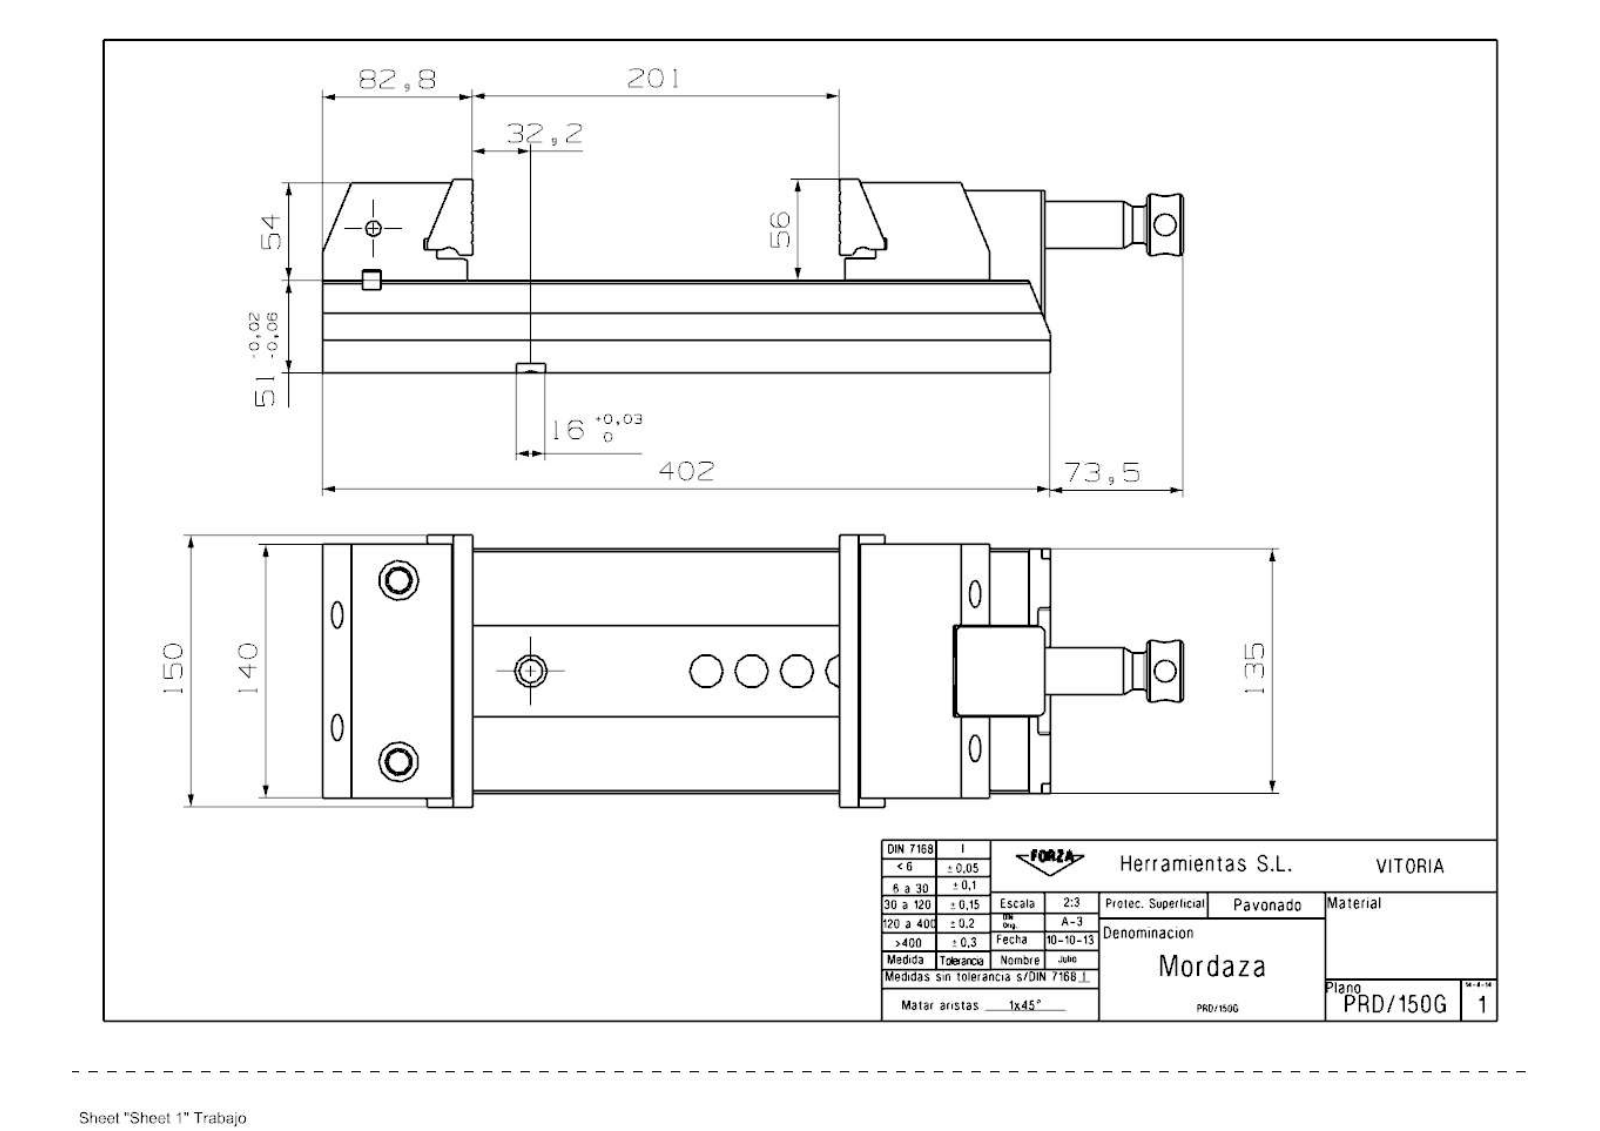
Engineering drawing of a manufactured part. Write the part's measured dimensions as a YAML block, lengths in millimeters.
part_name: "PRD_150G_Mordaza"
step_written_by: "SIEMENS PLM Software NX 9.0 (CONFIG_CONTROL_DESIGN)"
units: millimeters
bodies: {solids: 12, faces: 425, planar: 285, cylindrical: 92, other: 48}
overall_size: [475.5, 150, 107.1]
volume: 3171000
surface_area: 447778
round_holes:
  - {diameter: 13, count: 6}
  - {diameter: 15, count: 6}
  - {diameter: 5.19, count: 5}
  - {diameter: 6.99, count: 4}
  - {diameter: 8.5, count: 4}
  - {diameter: 8.78, count: 4}
  - {diameter: 10.58, count: 4}
  - {diameter: 19, count: 4}
  - {diameter: 9.7, count: 2}
  - {diameter: 10, count: 2}
  - {diameter: 12, count: 2}
  - {diameter: 12.38, count: 2}
round_bosses_or_shafts:
  - {diameter: 34, count: 1}
  - {diameter: 33.8, count: 1}
  - {diameter: 26, count: 1}
  - {diameter: 20, count: 1}
  - {diameter: 16.5, count: 1}
partial_cylinders:
  - {radius: 1.5, count: 4}
  - {radius: 8, count: 4}
  - {radius: 20, count: 4}
  - {radius: 1.6, count: 2}
  - {radius: 5.5, count: 2}
  - {radius: 6, count: 2}
  - {radius: 4, count: 1}
  - {radius: 9, count: 1}
face_to_face_distances: [51, 19.3, 31.7, 105, 49.4, 8, 1.6, 17.7, 135, 2.5]
hole_center_spacings: [11.5, 73.5, 85, 11.51, 95.17, 11.46, 22.27, 27.2]
